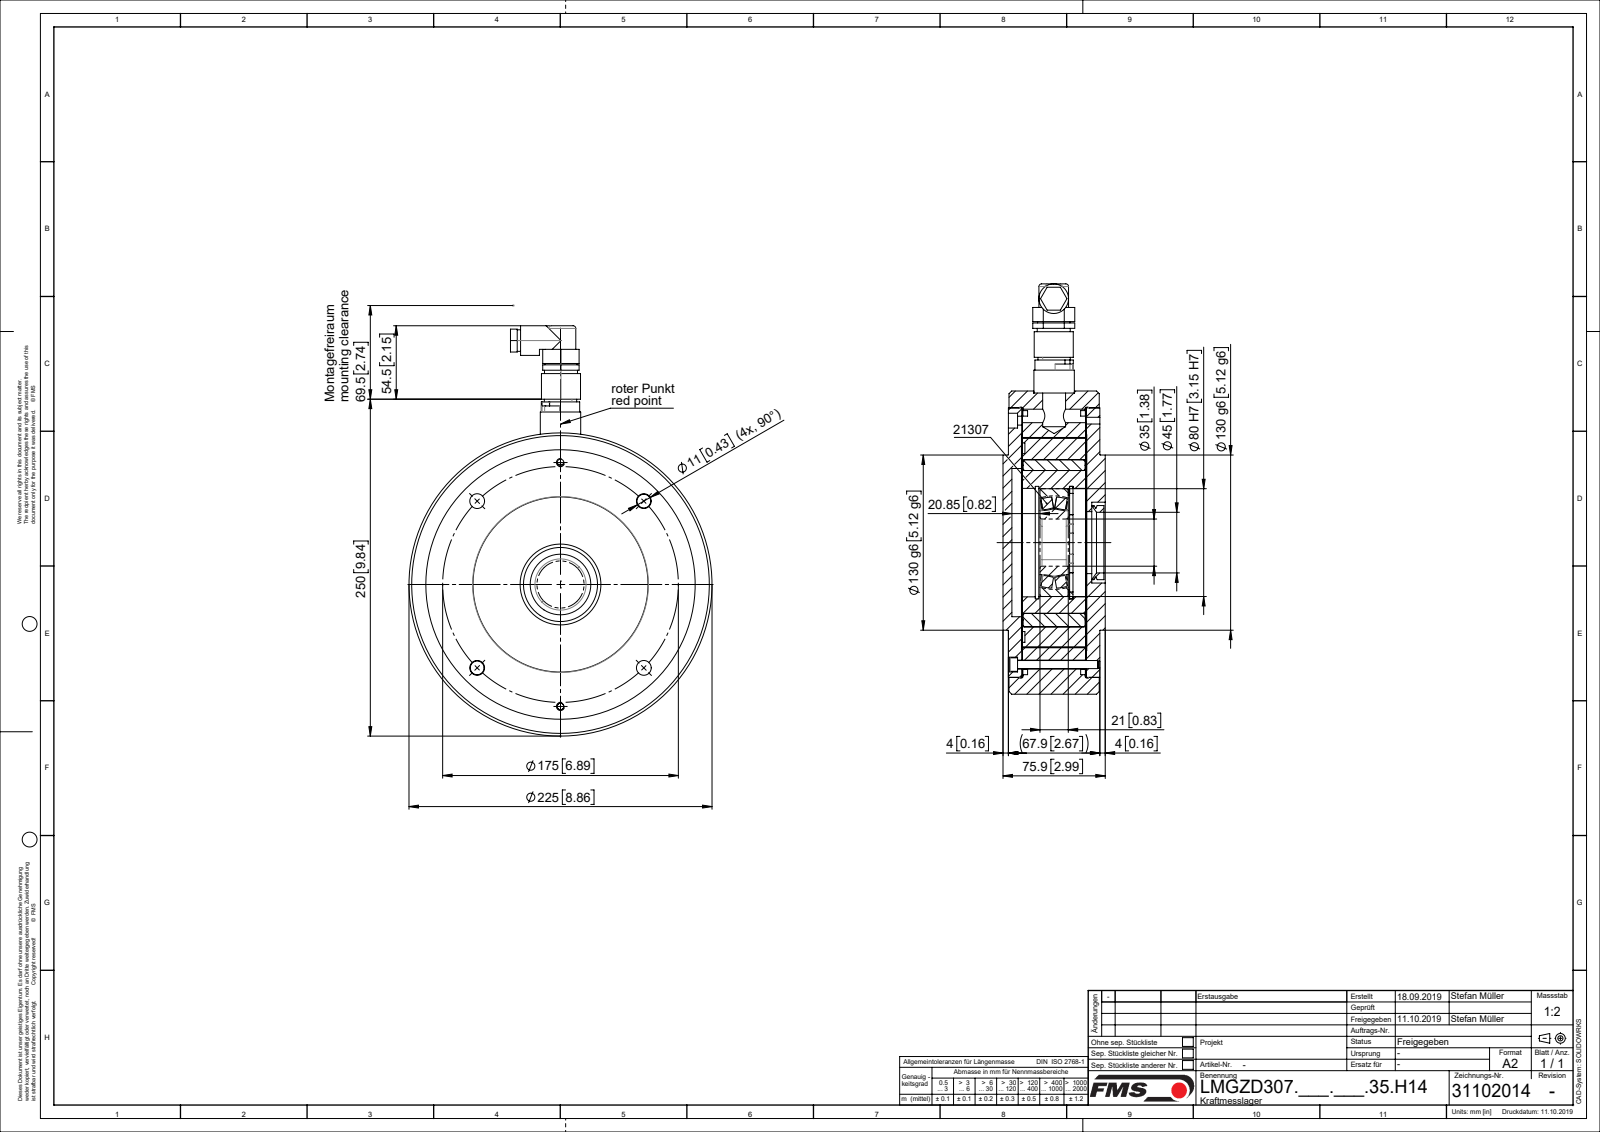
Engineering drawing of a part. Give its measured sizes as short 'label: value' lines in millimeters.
name: 49651-04_stp_01; 31101675_01; 31101677_V-045A; 43404.02_01 (+8 more)
written by: SolidWorks 2018 (CONFIG_CONTROL_DESIGN)
unit: mm
bodies: 47 solids, 777 faces (225 planar, 304 cylindrical, 248 other)
size: 304.5 × 225 × 75.9
volume: 2 442 000 mm³; area: 458 975 mm²
holes: 6× ⌀11, 4× ⌀2.5, 2× ⌀3, 2× ⌀3.4, 2× ⌀3.6, 2× ⌀5, 2× ⌀6.6, 2× ⌀10, 2× ⌀10.2, 1× ⌀8, 1× ⌀14, 1× ⌀17
bosses: 13× ⌀2.15, 2× ⌀24, 2× ⌀22, 2× ⌀5.5, 2× ⌀3, 1× ⌀225, 1× ⌀199, 1× ⌀188
rounds: 4× R0.1, 4× R11, 2× R2, 2× R3, 2× R4.91, 1× R33.25, 1× R79, 1× R82
face distances: 47.25, 10.2, 10.45, 57.45, 57.7, 48, 0.5, 0.75, 47.75, 9.7
hole spacings: 16.26, 22.47, 23, 62.02, 68.17, 87.5, 123.74, 134.45
